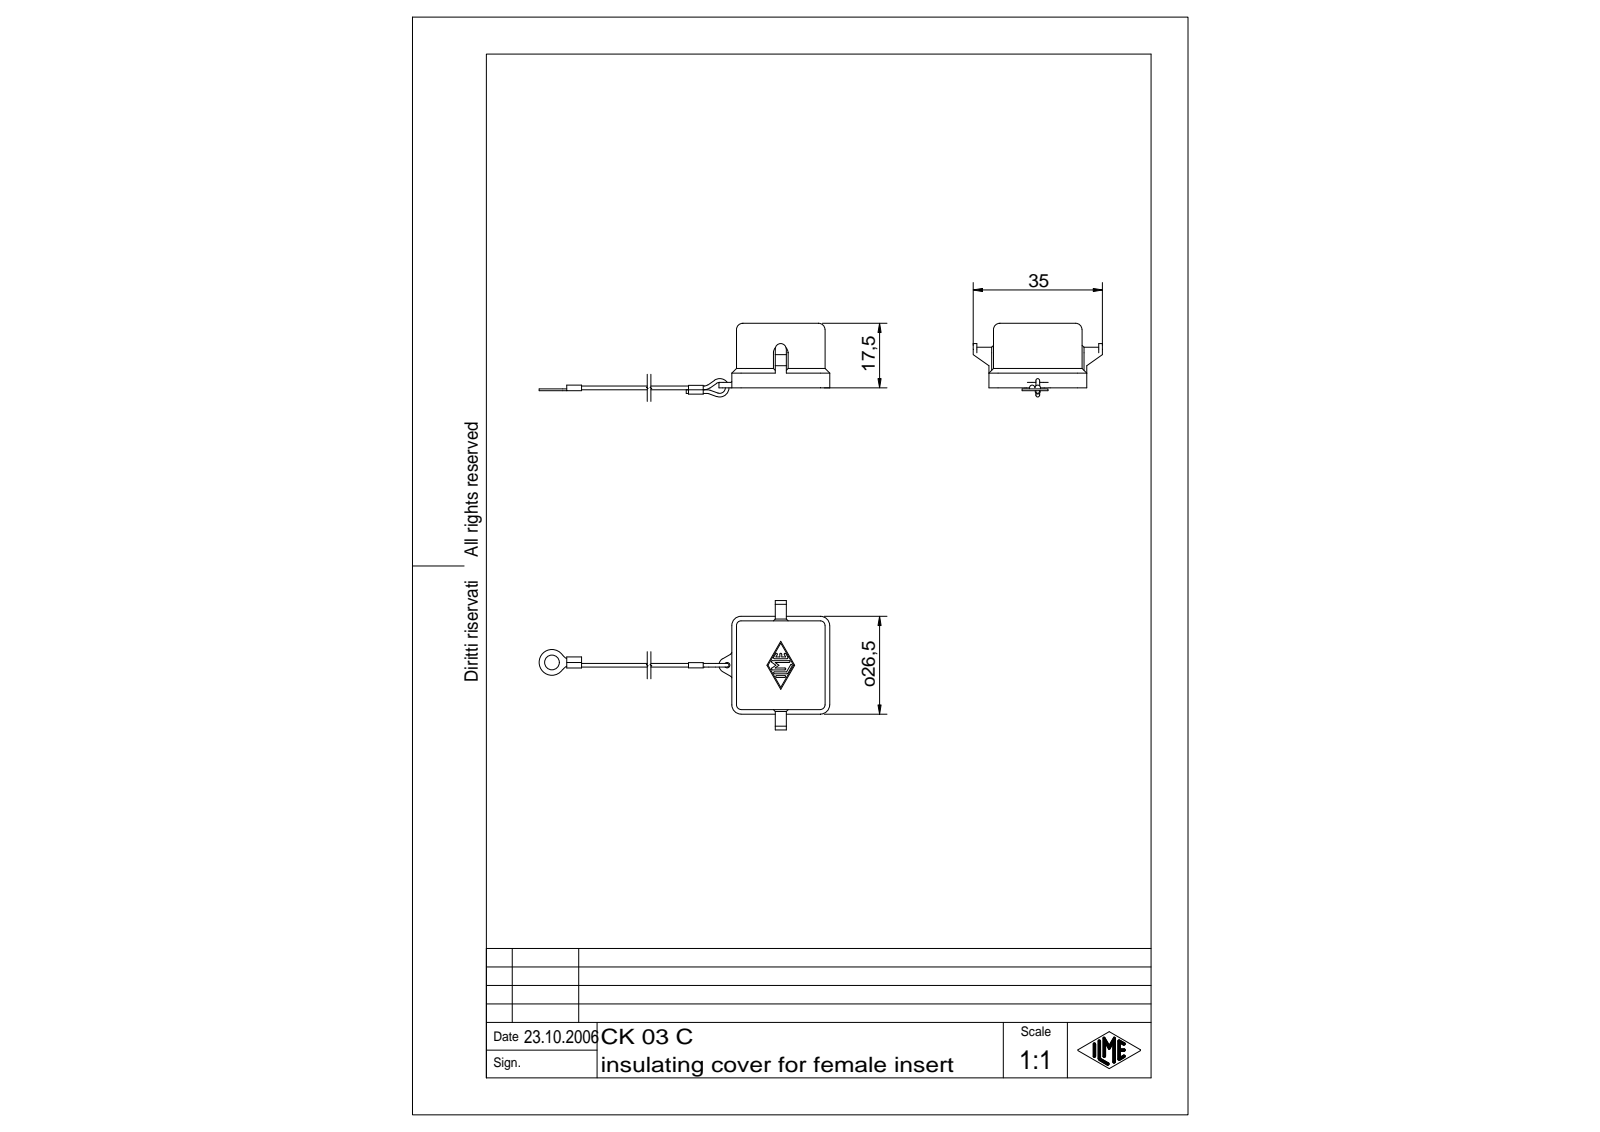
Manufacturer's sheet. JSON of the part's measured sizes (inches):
{"step_written_by": "Autodesk Inventor 7 (AUTOMOTIVE_DESIGN)", "units": "inches", "bodies": {"solids": 1, "faces": 231, "planar": 93, "cylindrical": 99, "other": 39}, "overall_size": [5.148, 1.378, 0.787], "volume_in3": 0.235, "surface_area_in2": 7.888, "round_holes": [[0.059, 1], [0.157, 1]], "round_bosses_or_shafts": [[0.039, 4], [0.276, 1]], "partial_cylinders_radius": [[0.01, 14], [0.069, 12], [0.008, 7], [0.049, 4], [0.098, 4], [0.126, 4], [0.02, 2], [0.028, 2]], "face_to_face_distances": [0.049, 0.896, 0.945, 0.846, 0.098, 0.079, 0.994, 0.148, 0.797, 0.551], "hole_center_spacings": [3.917]}
